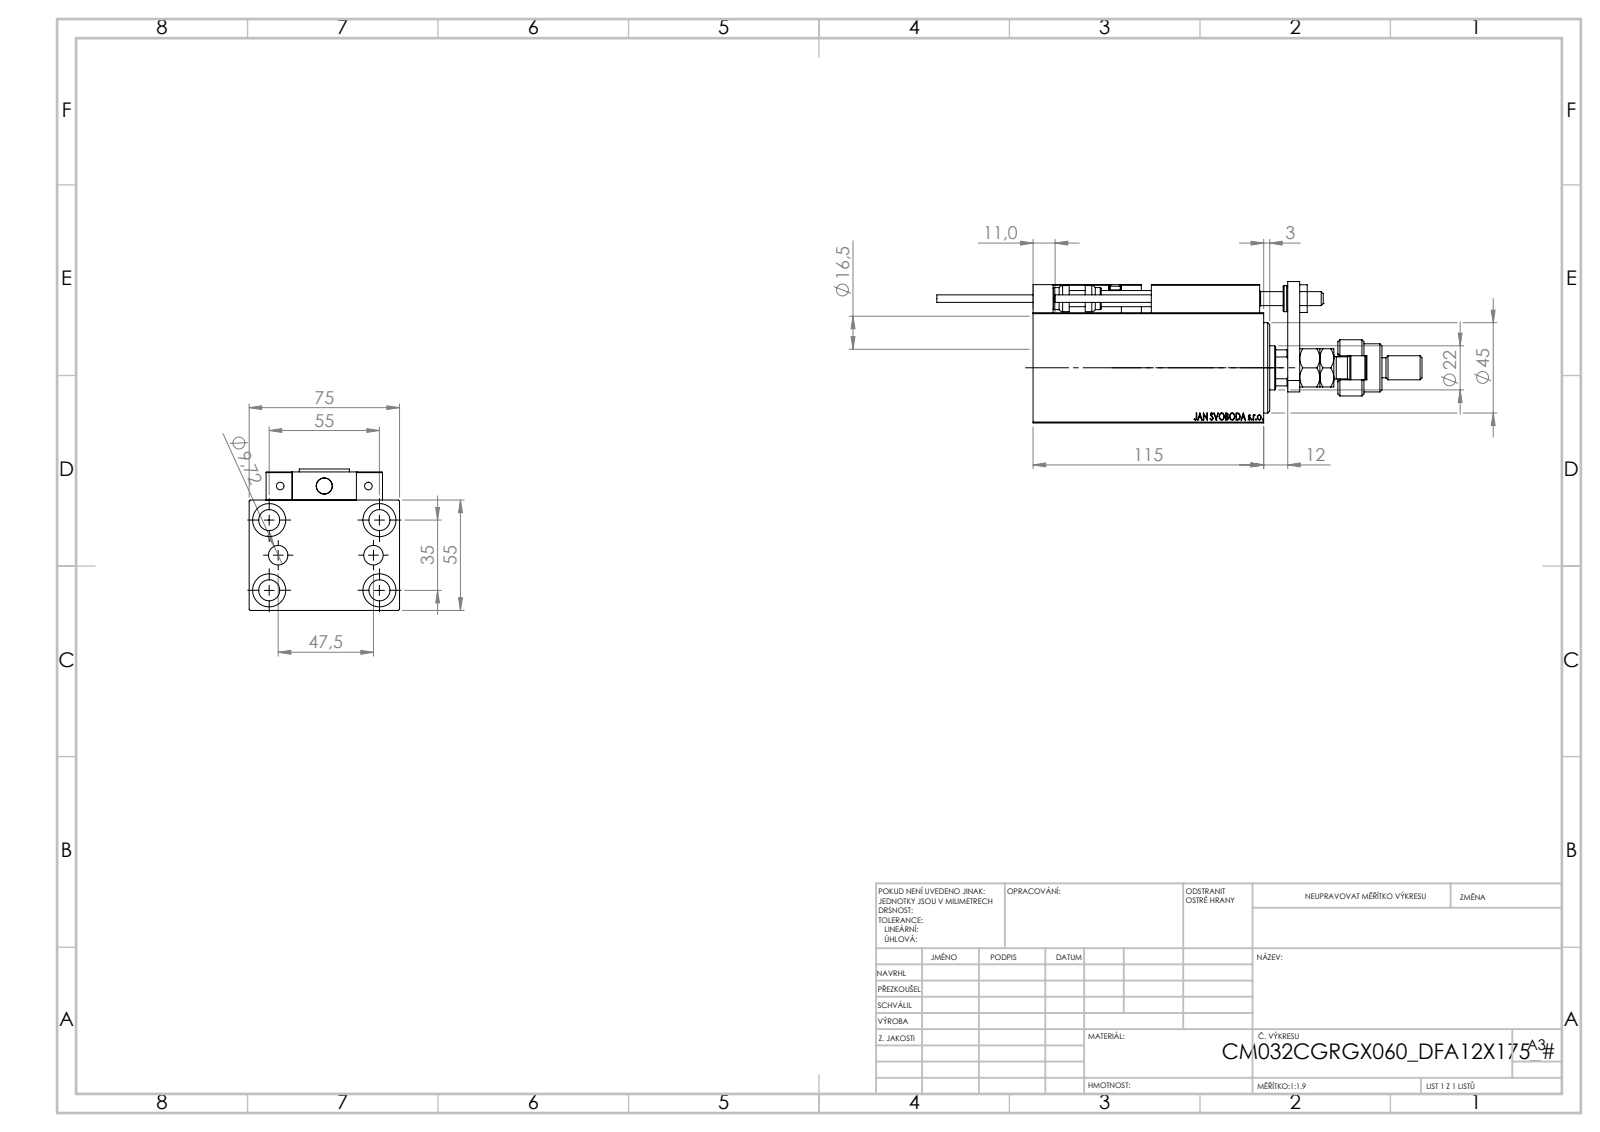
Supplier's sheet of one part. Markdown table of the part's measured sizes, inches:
| quantity | value |
| --- | --- |
| part name | TYC_L79; SWITCH_X_FRONT_BACK; V450CM_C_Body; V450CM_C_VCP (+7 more) |
| STEP written by | SolidWorks 2019 (CONFIG_CONTROL_DESIGN) |
| units | inches |
| bodies | 25 solids, 1363 faces (588 planar, 197 cylindrical, 578 other) |
| overall size | 9.528 × 2.953 × 2.776 |
| volume | 28.5 in³ |
| surface area | 174.9 in² |
| round holes (diameter × count) | 0.157 × 6, 0.315 × 5, 0.413 × 5, 0.65 × 5, 0.126 × 4, 0.197 × 2, 0.383 × 2, 0.276 × 1, 0.866 × 1, 1.004 × 1, 1.26 × 1, 1.339 × 1 |
| round bosses / shafts (diameter × count) | 0.433 × 2, 0.197 × 2, 0.15 × 2, 1.102 × 1, 0.945 × 1, 0.709 × 1, 0.512 × 1, 0.472 × 1 |
| partial cylindrical surfaces (radius × count) | 0.012 × 30, 0.118 × 2, 0.384 × 1, 0.413 × 1 |
| main face-to-face distances | 2.165, 2.953, 0.551, 0.197, 2.717, 0.709, 0.984, 0.236, 0.472, 0.394 |
| hole center spacings | 0.705, 1.283, 2.132, 0.448, 0.787, 0.935, 1.165, 1.169 |
